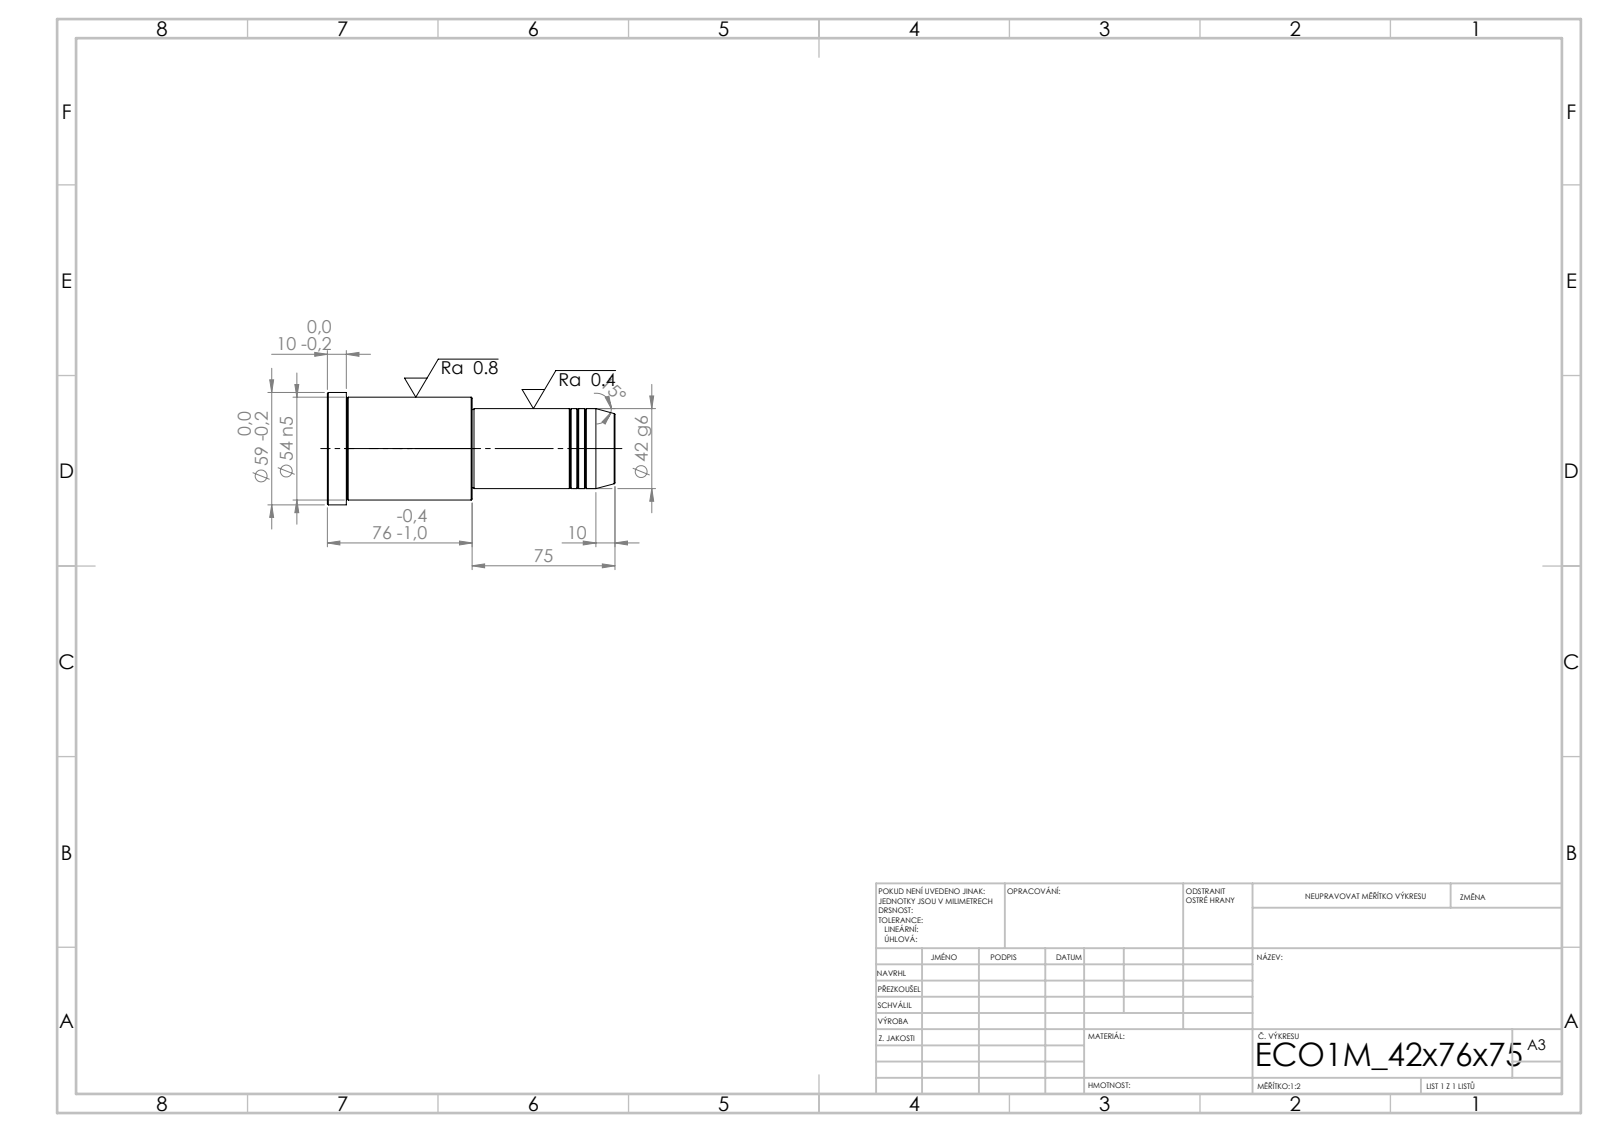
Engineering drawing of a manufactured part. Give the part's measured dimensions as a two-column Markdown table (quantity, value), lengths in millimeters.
| quantity | value |
| --- | --- |
| STEP written by | SolidWorks 2019 (CONFIG_CONTROL_DESIGN) |
| units | millimeters |
| bodies | 1 solid, 43 faces (5 planar, 14 cylindrical, 24 other) |
| overall size | 151 × 59 × 59 |
| volume | 280 377 mm³ |
| surface area | 28 362 mm² |
| round bosses / shafts (diameter × count) | 59 × 1, 54 × 1, 42 × 1, 41 × 1 |
| main face-to-face distances | 151, 75, 76, 141, 66, 10, 74, 1, 67, 77 |
